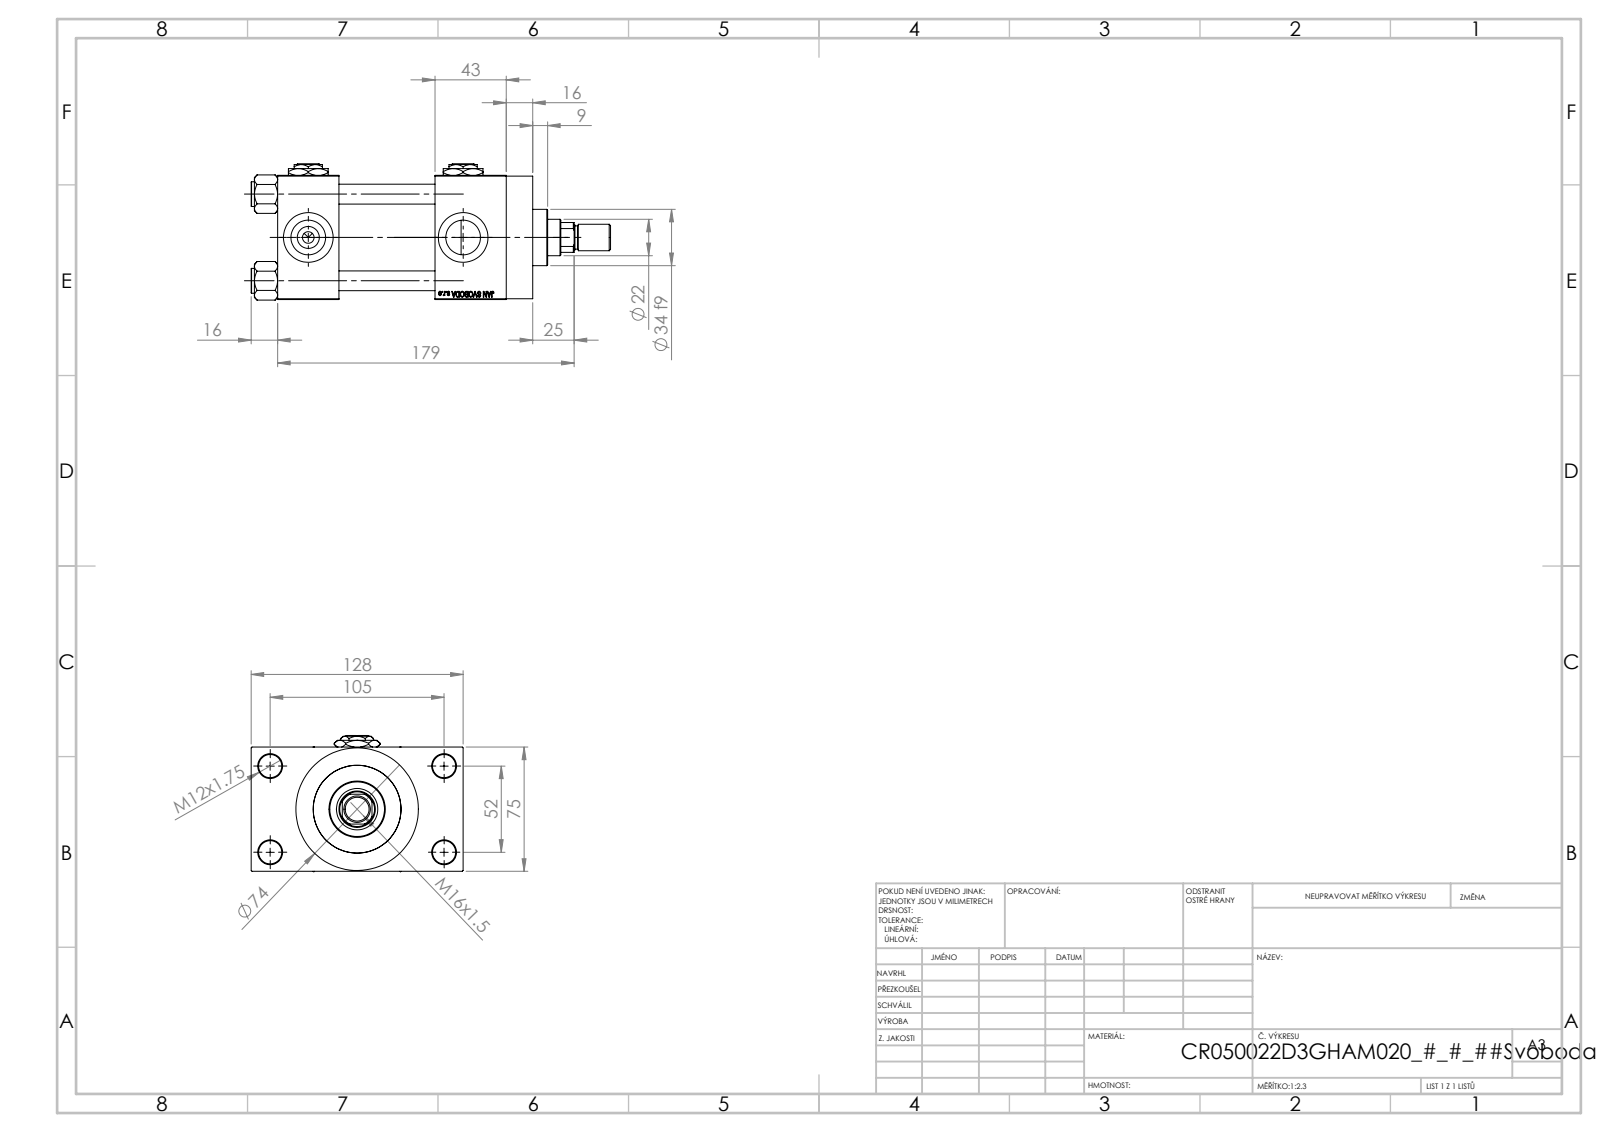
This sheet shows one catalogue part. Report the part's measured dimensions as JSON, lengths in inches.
{"part_name": "V215CR_D_Body; NUT_M5_D; V215CR_VCP_D; V215CR_D_TYCINKA (+3 more)", "step_written_by": "SolidWorks 2019 (CONFIG_CONTROL_DESIGN)", "units": "inches", "bodies": {"solids": 14, "faces": 1218, "planar": 549, "cylindrical": 103, "other": 566}, "overall_size": [8.543, 5.039, 3.239], "volume_in3": 48.66, "surface_area_in2": 267.3, "round_holes": [[0.472, 4], [0.551, 4], [0.825, 4], [1.181, 4], [0.276, 3], [0.413, 1], [0.866, 1], [0.984, 1], [1.614, 1], [1.969, 1], [2.087, 1]], "round_bosses_or_shafts": [[0.591, 4], [2.913, 1], [2.205, 1], [1.339, 1], [0.63, 1], [0.551, 1]], "partial_cylinders_radius": [[0.413, 1]], "face_to_face_distances": [2.953, 2.283, 1.457, 3.74, 1.043, 3.976, 5.433, 1.693, 3.996, 0.63], "hole_center_spacings": [1.037, 1.456, 2.059, 2.3, 2.307, 3.096, 3.715, 2.047]}
